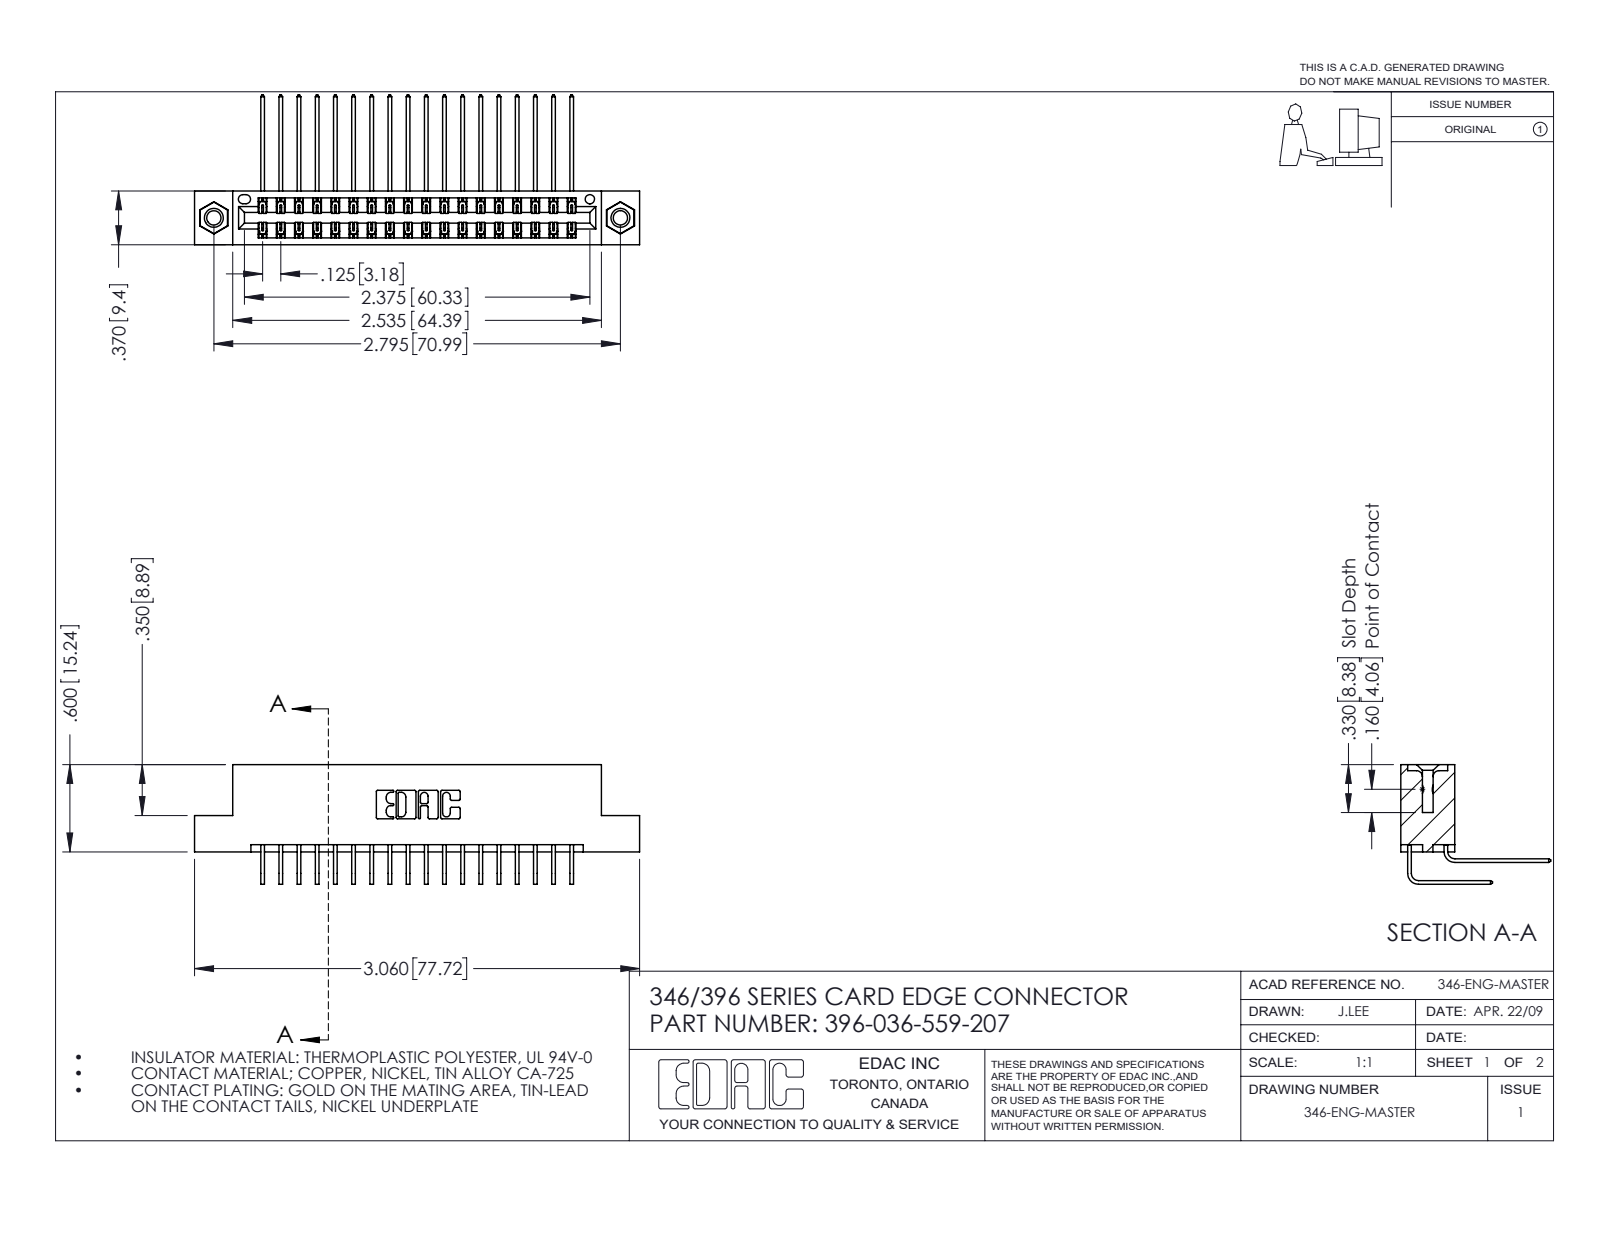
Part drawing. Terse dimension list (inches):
name: 345-292-001_558 559 Tail - 1; 345-250-001_345-250-005-103; 396-036-559-207; 346 Part_Flush Mounting Lugs - 0.156 Dia-TI (+1 more)
written by: SolidWorks 2016 (CONFIG_CONTROL_DESIGN)
unit: in
bodies: 39 solids, 2126 faces (1440 planar, 670 cylindrical, 16 other)
size: 3.06 × 1.03 × 0.823
volume: 0.463 in³; area: 17.18 in²
holes: 2× ⌀0.098, 2× ⌀0.125, 2× ⌀0.156, 1× ⌀0.064
bosses: 2× ⌀0.155
rounds: 54× R0.006, 22× R0.01, 6× R0.007, 6× R0.031, 3× R0.026, 2× R0.014, 2× R0.022, 2× R0.024
face distances: 0.048, 0.322, 0.25, 0.025, 0.37, 0.072, 0.298, 0.275, 0.148, 0.222
hole spacings: 0.246, 2.588, 2.795
